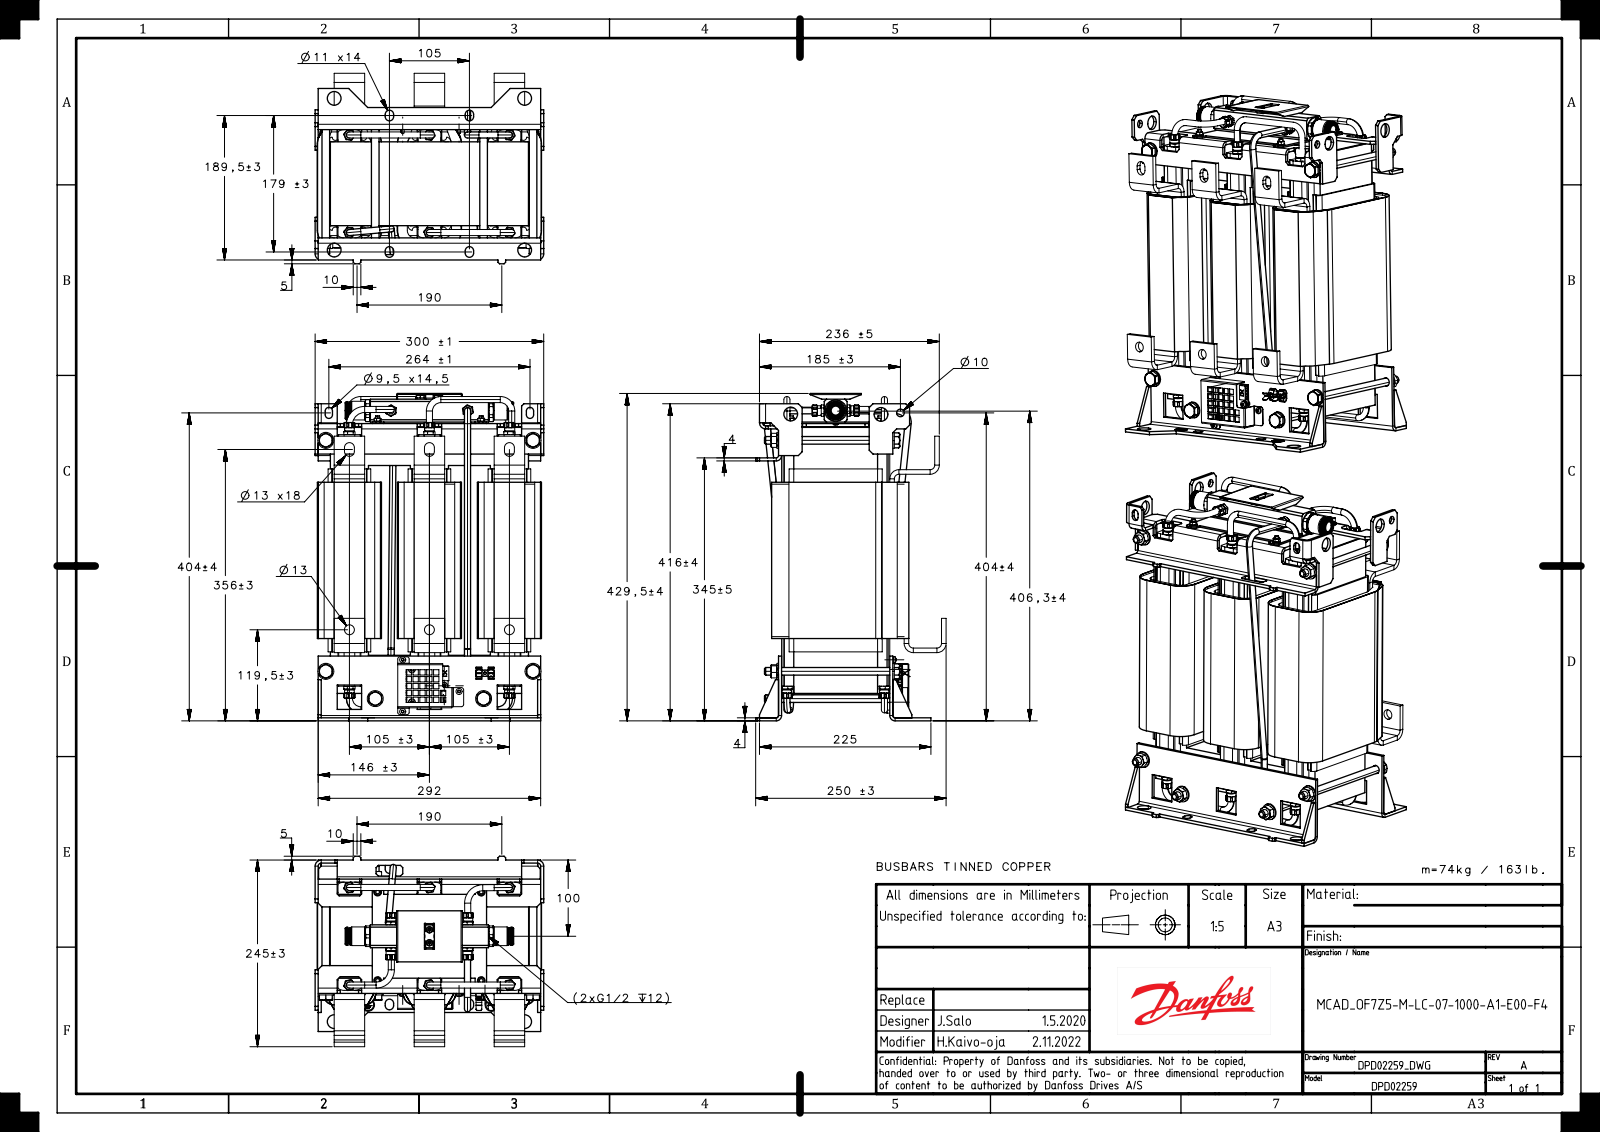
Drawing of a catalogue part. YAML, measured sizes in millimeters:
part_name: "U3193C6C63D8b3mw"
step_written_by: "SIEMENS PLM Software NX 1892 (AUTOMOTIVE_DESIGN)"
units: millimeters
bodies: {solids: 191, faces: 6694, planar: 4276, cylindrical: 1714, other: 704}
overall_size: [429.5, 300, 249.91]
volume: 13100000
surface_area: 3146000
round_holes:
  - {diameter: 6, count: 26}
  - {diameter: 5, count: 9}
  - {diameter: 4.8, count: 8}
  - {diameter: 8.3, count: 8}
  - {diameter: 8.8, count: 8}
  - {diameter: 10.5, count: 8}
  - {diameter: 11, count: 8}
  - {diameter: 10, count: 7}
  - {diameter: 18, count: 6}
  - {diameter: 3.3, count: 5}
  - {diameter: 3.6, count: 4}
  - {diameter: 5.3, count: 4}
round_bosses_or_shafts:
  - {diameter: 8, count: 28}
  - {diameter: 1, count: 15}
  - {diameter: 21, count: 8}
  - {diameter: 12.74, count: 8}
  - {diameter: 11, count: 8}
  - {diameter: 9.6, count: 8}
  - {diameter: 8.5, count: 8}
  - {diameter: 4, count: 7}
partial_cylinders:
  - {radius: 1.2, count: 96}
  - {radius: 0.5, count: 67}
  - {radius: 0.36, count: 24}
  - {radius: 0.78, count: 24}
  - {radius: 1, count: 22}
  - {radius: 2, count: 22}
  - {radius: 0.55, count: 18}
  - {radius: 0.75, count: 16}
face_to_face_distances: [105, 16.91, 66.91, 210, 50, 121.91, 171.91, 88.09, 38.09, 6]
hole_center_spacings: [105, 128, 165.56, 3, 14.71, 37.48, 65.12, 68.26]
